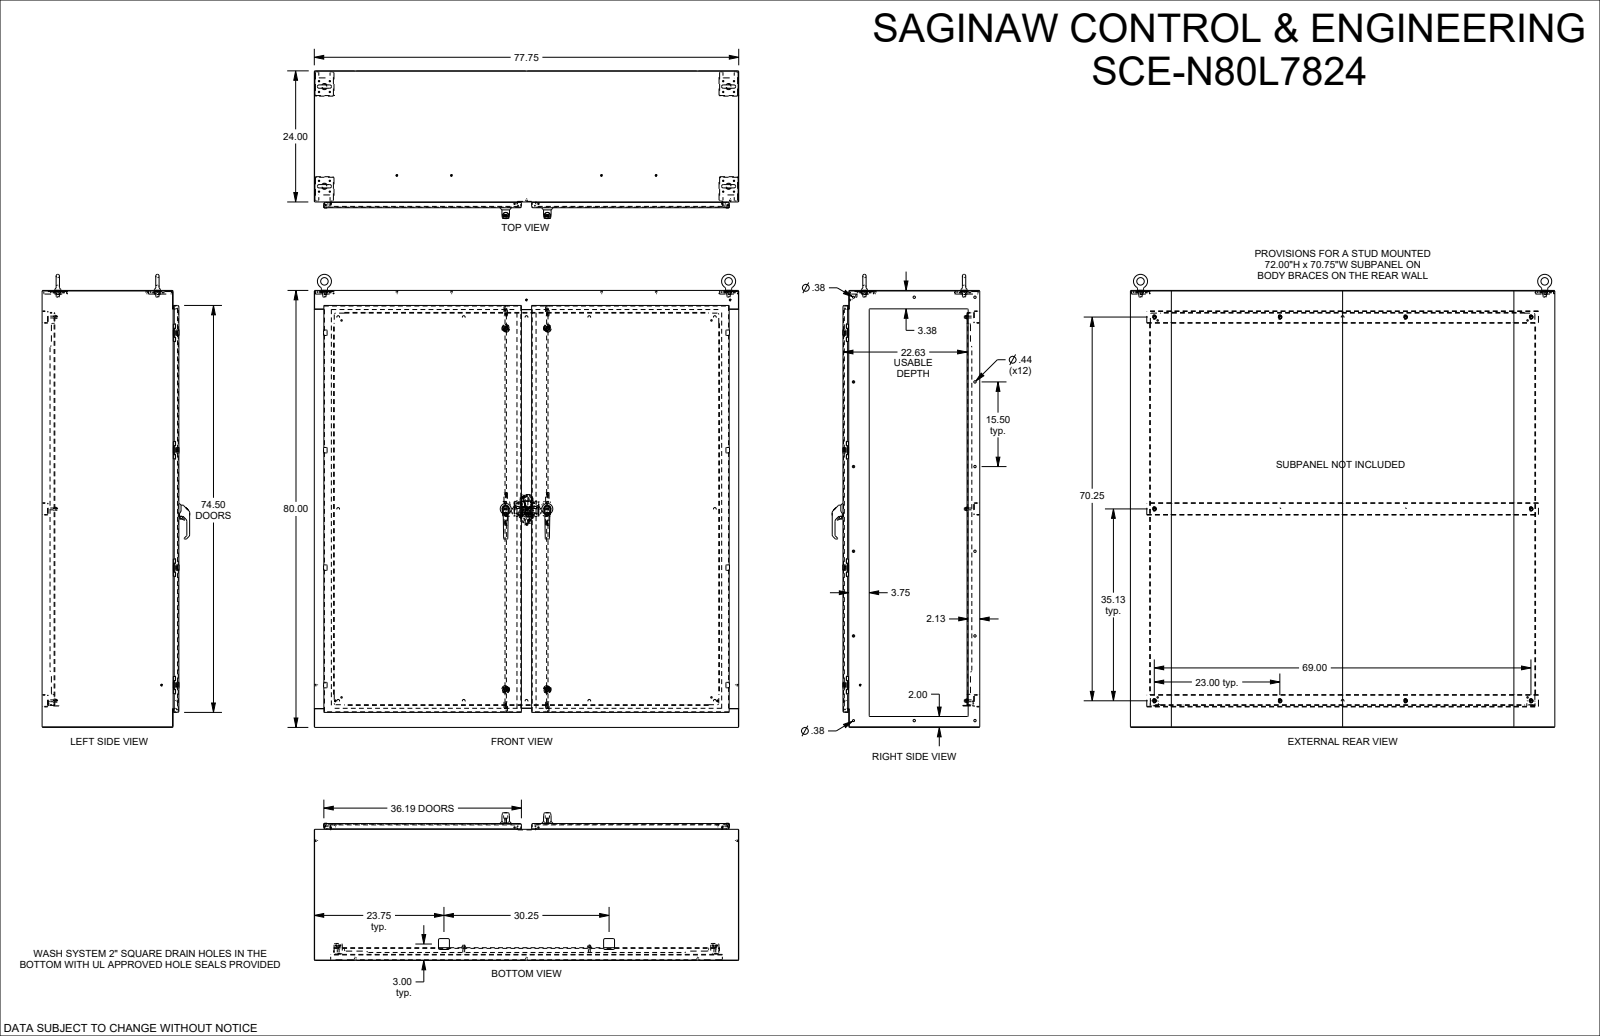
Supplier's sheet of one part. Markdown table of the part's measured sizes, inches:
| quantity | value |
| --- | --- |
| part name | SCE-N80L7824 |
| STEP written by | SolidWorks 2023 (AUTOMOTIVE_DESIGN) |
| units | inches |
| bodies | 51 solids, 8071 faces (3220 planar, 2778 cylindrical, 2073 other) |
| overall size | 82.945 × 77.75 × 27.046 |
| volume | 2 252 in³ |
| surface area | 42 993 in² |
| round holes (diameter × count) | 0.25 × 20, 0.375 × 18, 0.205 × 16, 0.244 × 16, 0.437 × 12, 0.04 × 8, 0.17 × 8, 0.218 × 8, 0.256 × 4, 0.343 × 4, 0.344 × 4, 0.36 × 4 |
| round bosses / shafts (diameter × count) | 0.17 × 24, 0.25 × 20, 0.24 × 16, 0.196 × 10, 1.4 × 4, 1.173 × 4, 0.6 × 4, 0.341 × 4 |
| partial cylindrical surfaces (radius × count) | 0.015 × 296, 0.03 × 226, 0.125 × 102, 0.02 × 74, 0.02 × 48, 0.039 × 42, 0.25 × 42, 0.04 × 40 |
| main face-to-face distances | 0.104, 24.954, 25.058, 24.85, 79.896, 23.896, 1.058, 80, 79.792, 23.792 |
| hole center spacings | 21.5, 1.979, 15.5, 27.117, 1.4, 31, 38.159, 43 |
